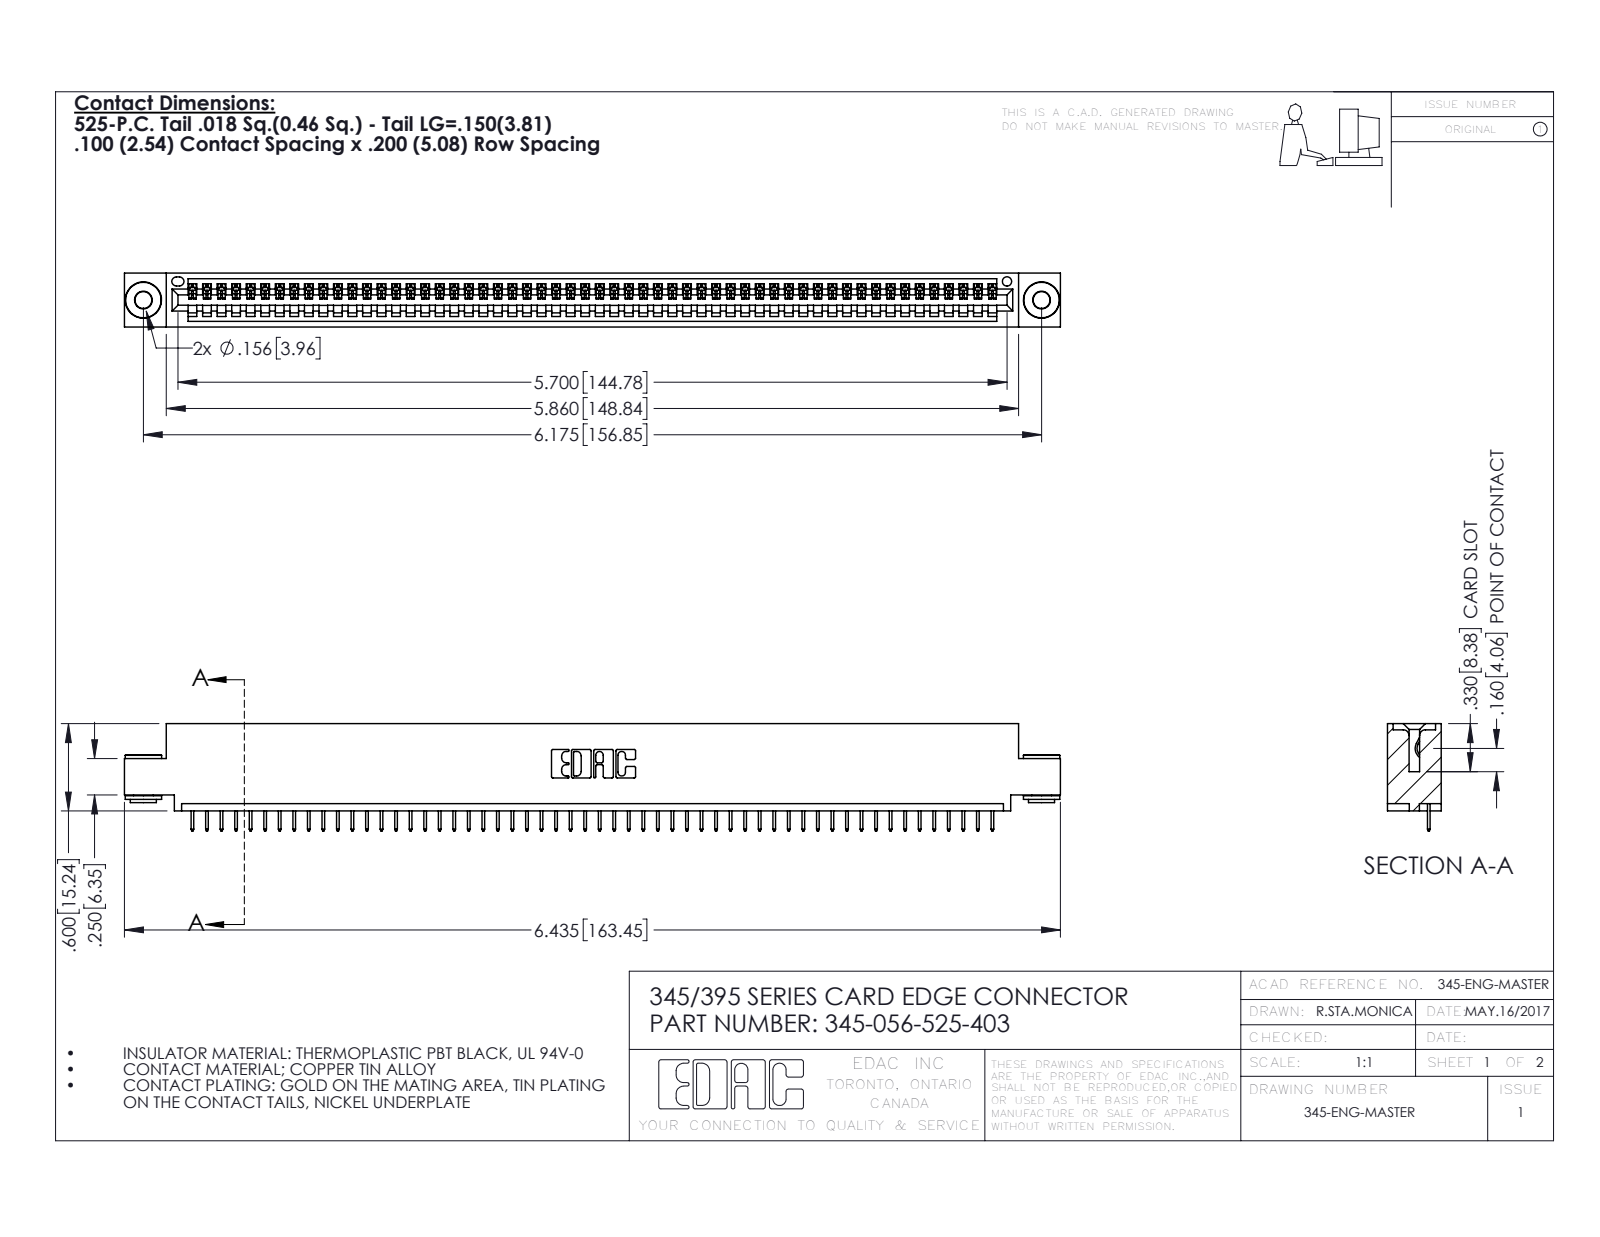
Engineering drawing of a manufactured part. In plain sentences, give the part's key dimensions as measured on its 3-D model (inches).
The part is named "345-056-525-403; 345-292-001_345-293-125; 345-250-002_345-250-002-102; 345 Part_0.110 Offset - 0.156 Dia-TH". Its 3-D file was written by "SolidWorks 2020 (CONFIG_CONTROL_DESIGN)". It is 59 solids with 3640 faces: 2670 planar, 962 cylindrical and 8 other. Overall it measures 6.435 by 0.737 by 0.37 inches. Its volume is 0.937 cubic inches and its surface area 31.2 square inches. Round holes: 2 of diameter 0.116, 2 of diameter 0.156, 1 of diameter 0.064. Round bosses or shafts: 2 of diameter 0.25, 2 of diameter 0.18, 2 of diameter 0.136. Partial cylindrical surfaces (rounded edges, fillets, slot ends): 112 of radius 0.006, 22 of radius 0.01, 6 of radius 0.007, 6 of radius 0.031, 3 of radius 0.026, 2 of radius 0.031, 2 of radius 0.04, 1 of radius 0.014. The main face-to-face distances are 0.072, 0.298, 0.37, 0.2, 0.025, 0.098, 0.272, 0.225, 0.072, 0.149. The hole center spacings are 0.27, 5.939, 6.175.
